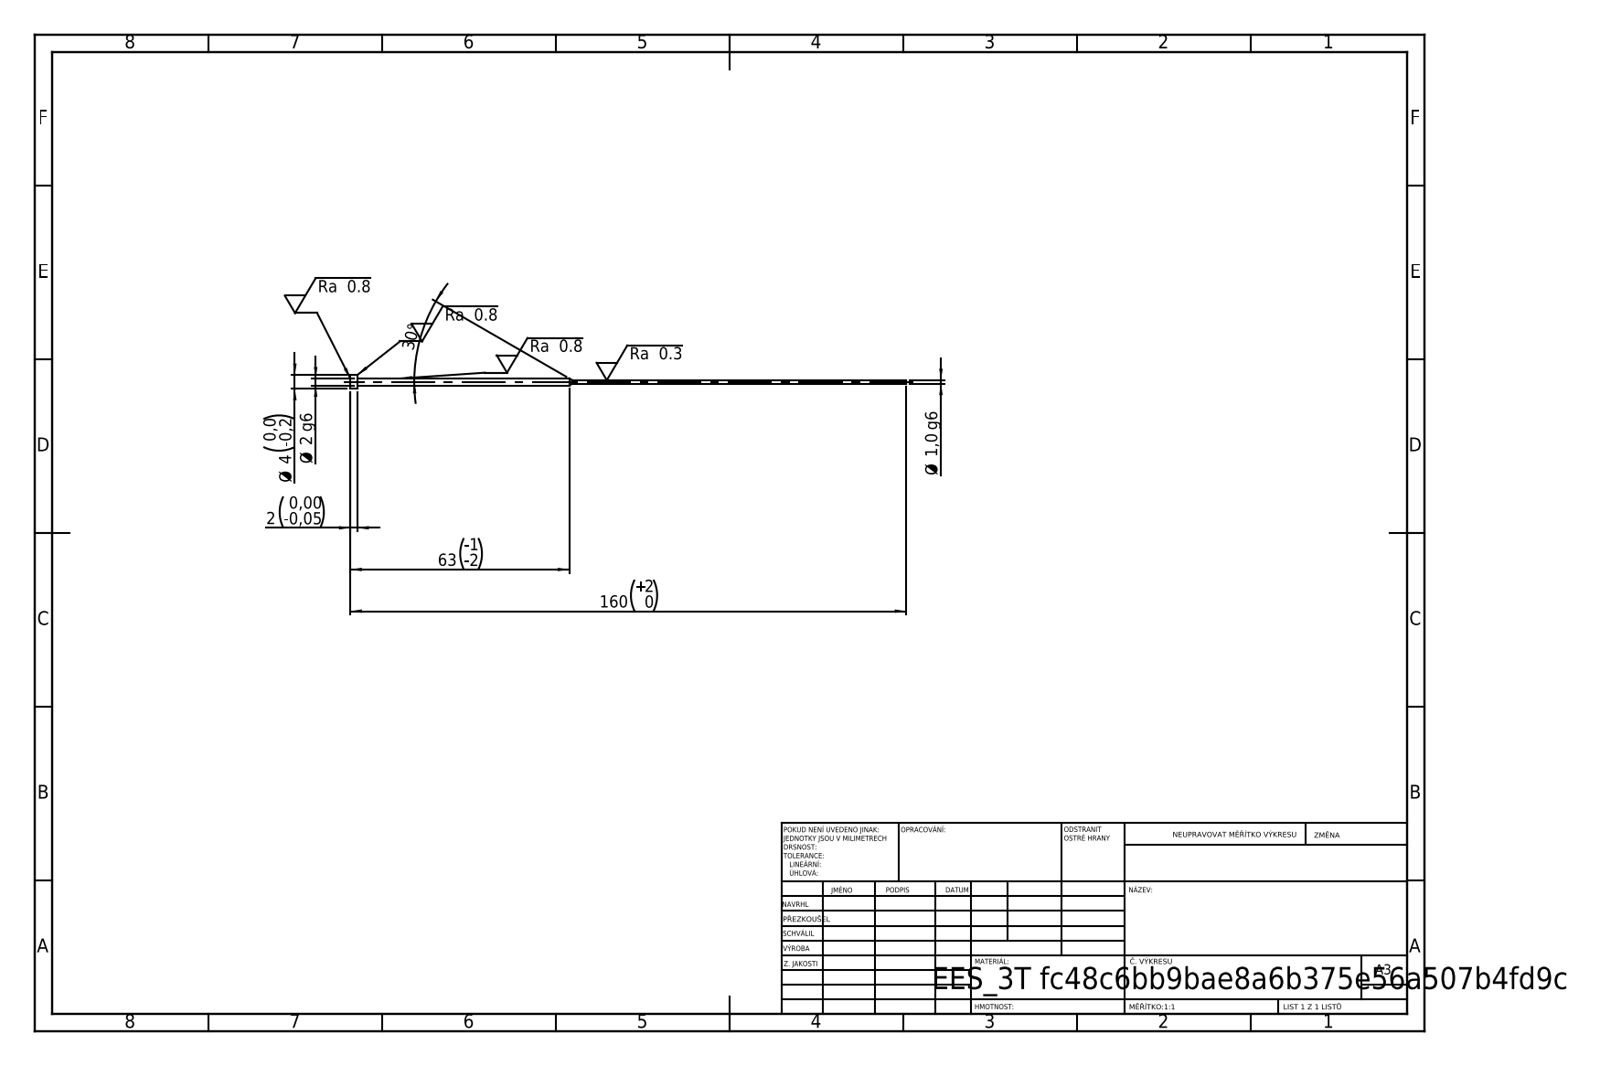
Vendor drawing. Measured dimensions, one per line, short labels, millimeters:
written by: SolidWorks 2019 (CONFIG_CONTROL_DESIGN)
unit: mm
bodies: 1 solid, 11 faces (3 planar, 6 cylindrical, 2 other)
size: 160 × 4 × 4
volume: 294 mm³; area: 738 mm²
bosses: 1× ⌀4, 1× ⌀2, 1× ⌀1
face distances: 2, 158, 160
